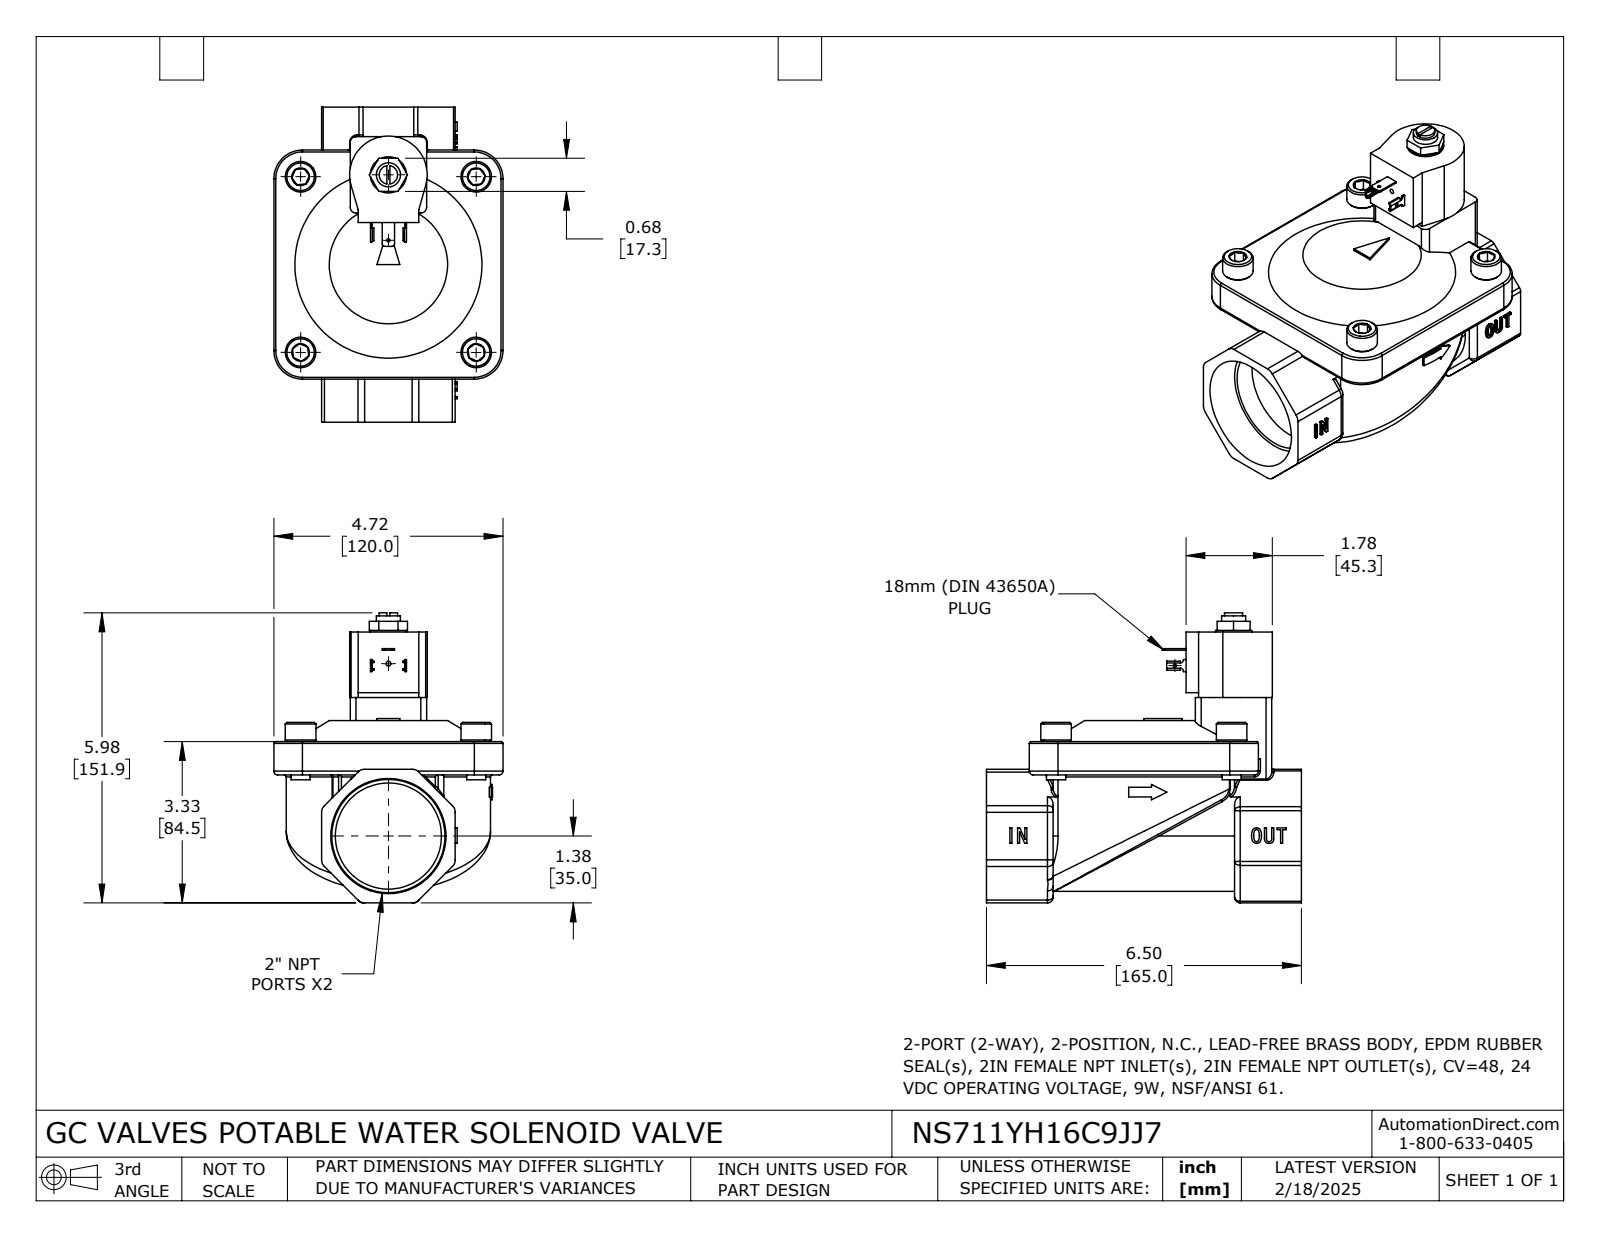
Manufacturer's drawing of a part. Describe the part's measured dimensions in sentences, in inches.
The part is named "NS711YH16C9JJ7". Its 3-D file was written by "SolidWorks 2024 (CONFIG_CONTROL_DESIGN)". It is 1 solid with 474 faces: 206 planar, 135 cylindrical and 133 other. Overall it measures 6.496 by 5.979 by 4.724 inches. Its volume is 55.95 cubic inches and its surface area 147.1 square inches. Round holes: 1 of diameter 0.066, 1 of diameter 0.067, 1 of diameter 0.1, 1 of diameter 2.188. Round bosses or shafts: 4 of diameter 0.63, 4 of diameter 0.394, 1 of diameter 0.746, 1 of diameter 0.499, 1 of diameter 0.38. Partial cylindrical surfaces (rounded edges, fillets, slot ends): 28 of radius 0.118, 21 of radius 0.039, 10 of radius 0.197, 4 of radius 0.006, 4 of radius 0.041, 4 of radius 0.079, 4 of radius 0.591, 2 of radius 0.05. The main face-to-face distances are 0.689, 2.756, 3.74, 0.433, 1.575, 1.122, 0.984, 2.756, 4.724, 5.61. The hole center spacings are 3.554.
